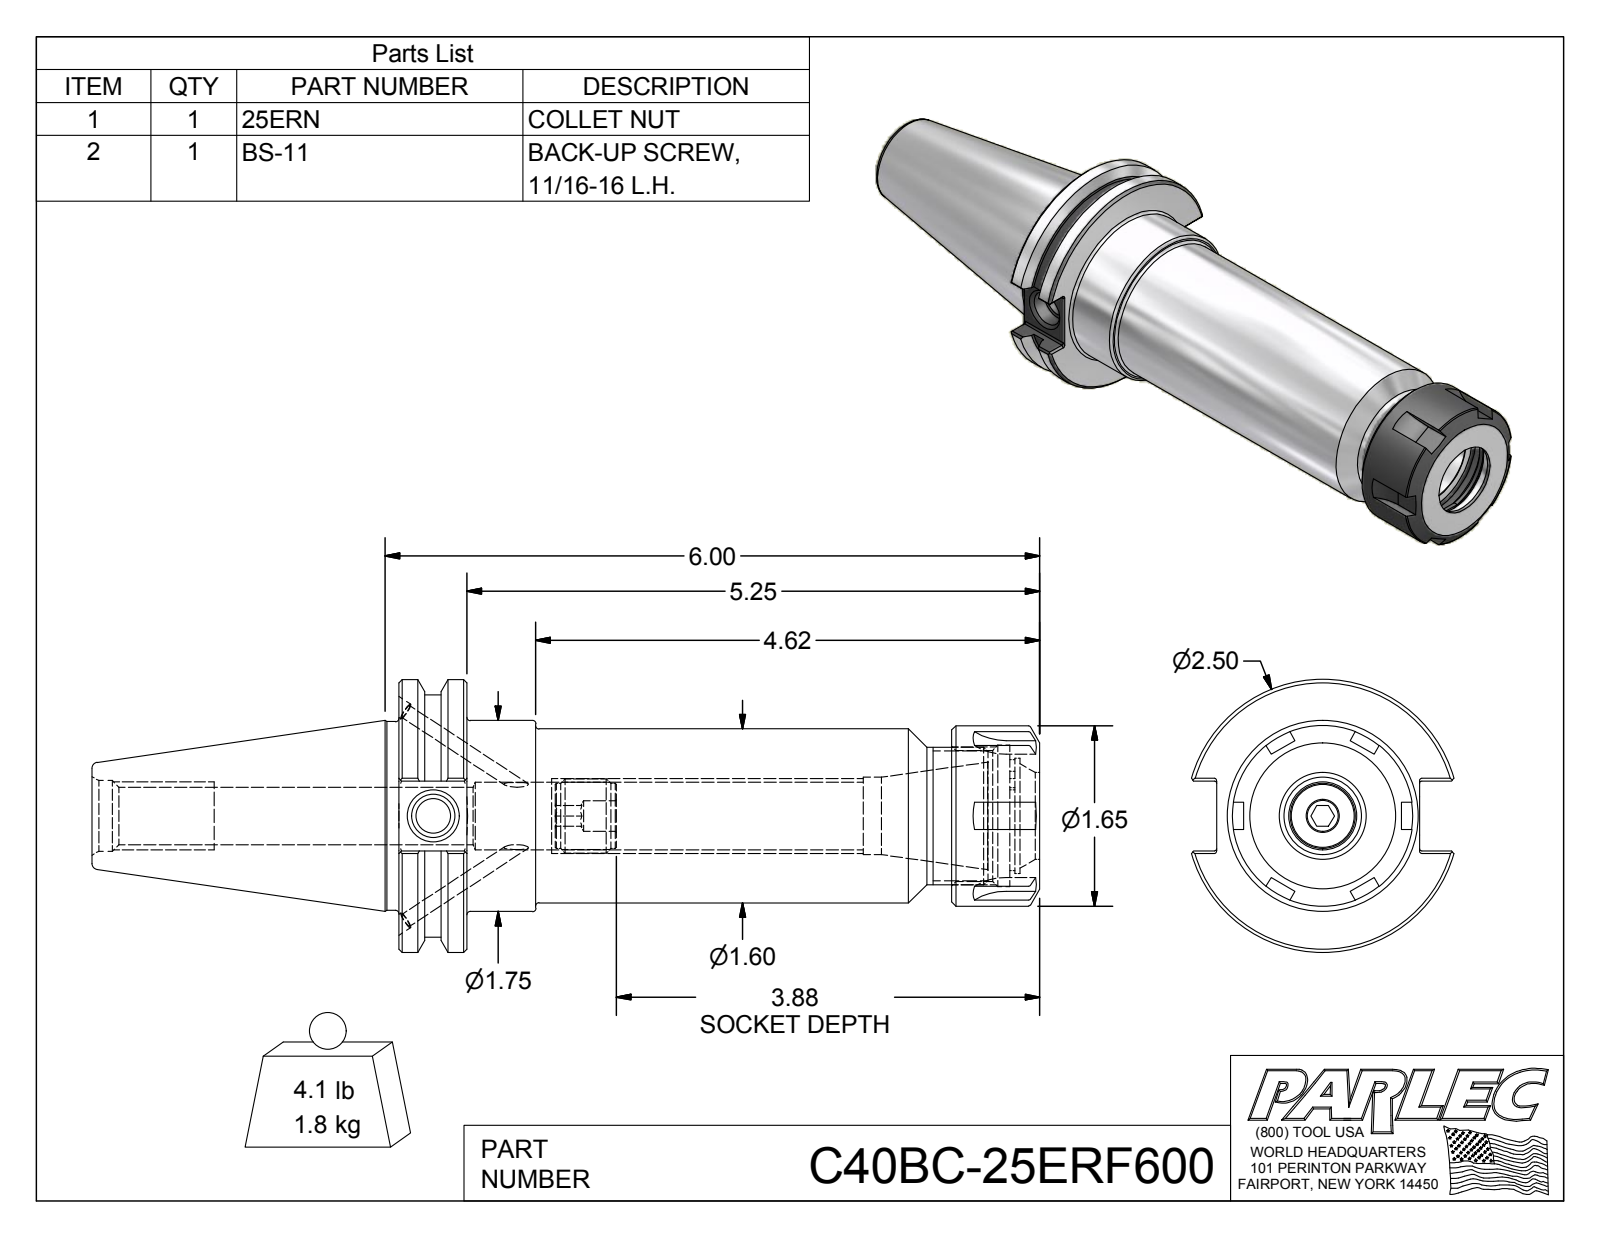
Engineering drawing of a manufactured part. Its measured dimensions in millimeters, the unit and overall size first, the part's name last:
Units: millimetres
Overall size (bounding box): 220.66 × 63.5 × 61.05
Round holes (diameter × count): ⌀3.3 ×2, ⌀4.1 ×2, ⌀7.11 ×1, ⌀8 ×1, ⌀10.13 ×1, ⌀13.39 ×1, ⌀15.75 ×1, ⌀16.46 ×1, ⌀18.03 ×1, ⌀20.32 ×1, ⌀30.5 ×1, ⌀32.88 ×1
Round bosses / shafts (diameter × count): ⌀4.2 ×2, ⌀4 ×2, ⌀63.5 ×1, ⌀56.36 ×1, ⌀44.45 ×1, ⌀43.94 ×1, ⌀42 ×1, ⌀40.51 ×1
Partial cylindrical surfaces — rounded edges, fillets, slot ends (radius × count): R0.51 ×24, R12 ×1, R13.06 ×1, R13.43 ×1
Main face-to-face distances: 15.87, 149.22, 133.35, 128.65, 112.78, 20.57, 142.12, 126.25, 13.47, 7.1
Volume: 240 463 mm³ · Surface area: 50 064 mm²
Bodies: 5 solids, 225 faces (98 planar, 61 cylindrical, 66 other)
Part name (STEP PRODUCT): C40BCB-25ER6-1; 029-965; 25ERN; BS-11 (+1 more)
STEP written by: Autodesk Inventor 2016 (AUTOMOTIVE_DESIGN)
